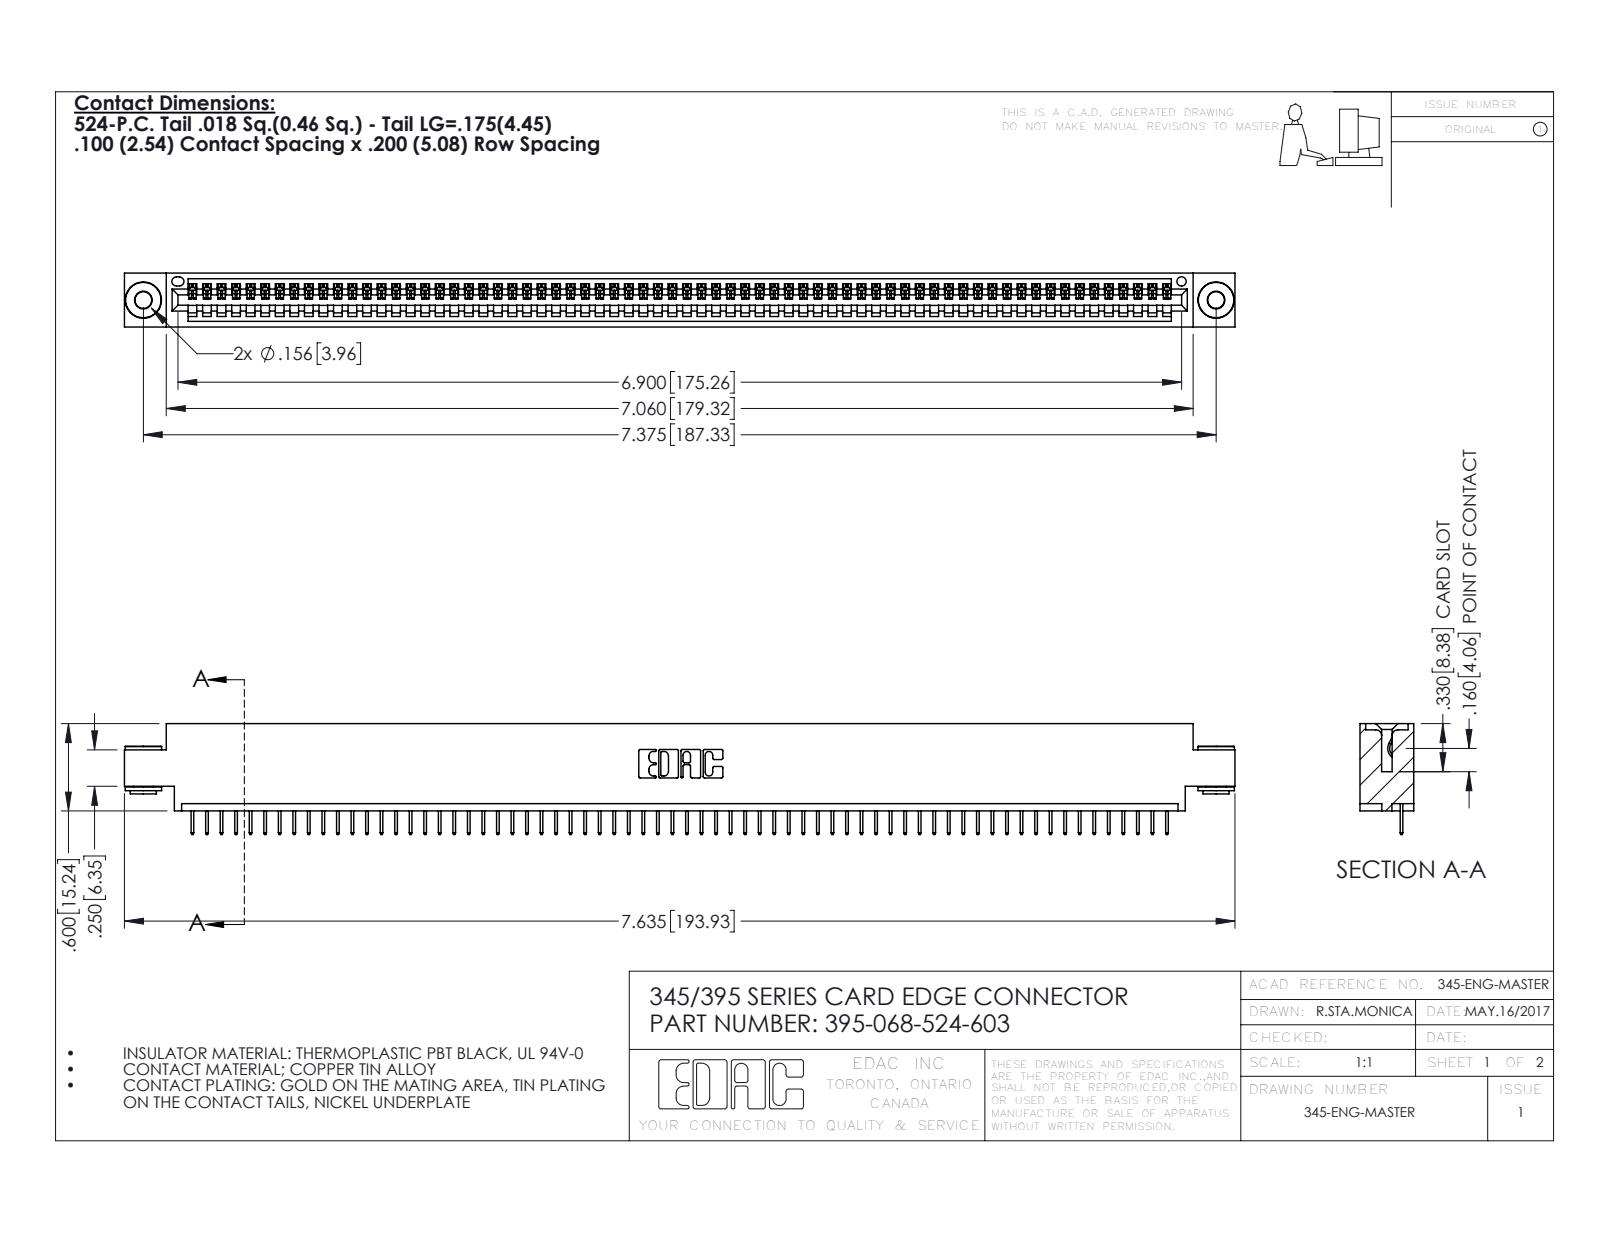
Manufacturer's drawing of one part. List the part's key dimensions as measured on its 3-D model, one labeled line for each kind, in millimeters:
Part name (STEP PRODUCT): 345-250-002_345-250-002-102; 395-068-524-603; 345-292-001_345-293-124; 345 Part_0.170 Offset - 0.156 Dia-TH
STEP written by: SolidWorks 2016 (CONFIG_CONTROL_DESIGN)
Units: millimetres
Bodies: 71 solids, 4384 faces (3222 planar, 1154 cylindrical, 8 other)
Overall size (bounding box): 193.9 × 19.4 × 9.4
Volume: 18 270 mm³ · Surface area: 24 120 mm²
Round holes (diameter × count): ⌀2.9 ×2, ⌀4 ×2, ⌀1.6 ×1
Round bosses / shafts (diameter × count): ⌀6.4 ×2, ⌀4.6 ×2, ⌀3.5 ×2
Partial cylindrical surfaces — rounded edges, fillets, slot ends (radius × count): R0.2 ×136, R0.3 ×22, R0.2 ×6, R0.8 ×6, R0.7 ×3, R0.8 ×2, R1 ×2, R0.4 ×1
Main face-to-face distances: 1.8, 7.6, 9.4, 5.1, 2.5, 6.9, 0.6, 5.7, 1.8, 4.4
Hole centre spacings: 6.9, 181.3, 187.3
